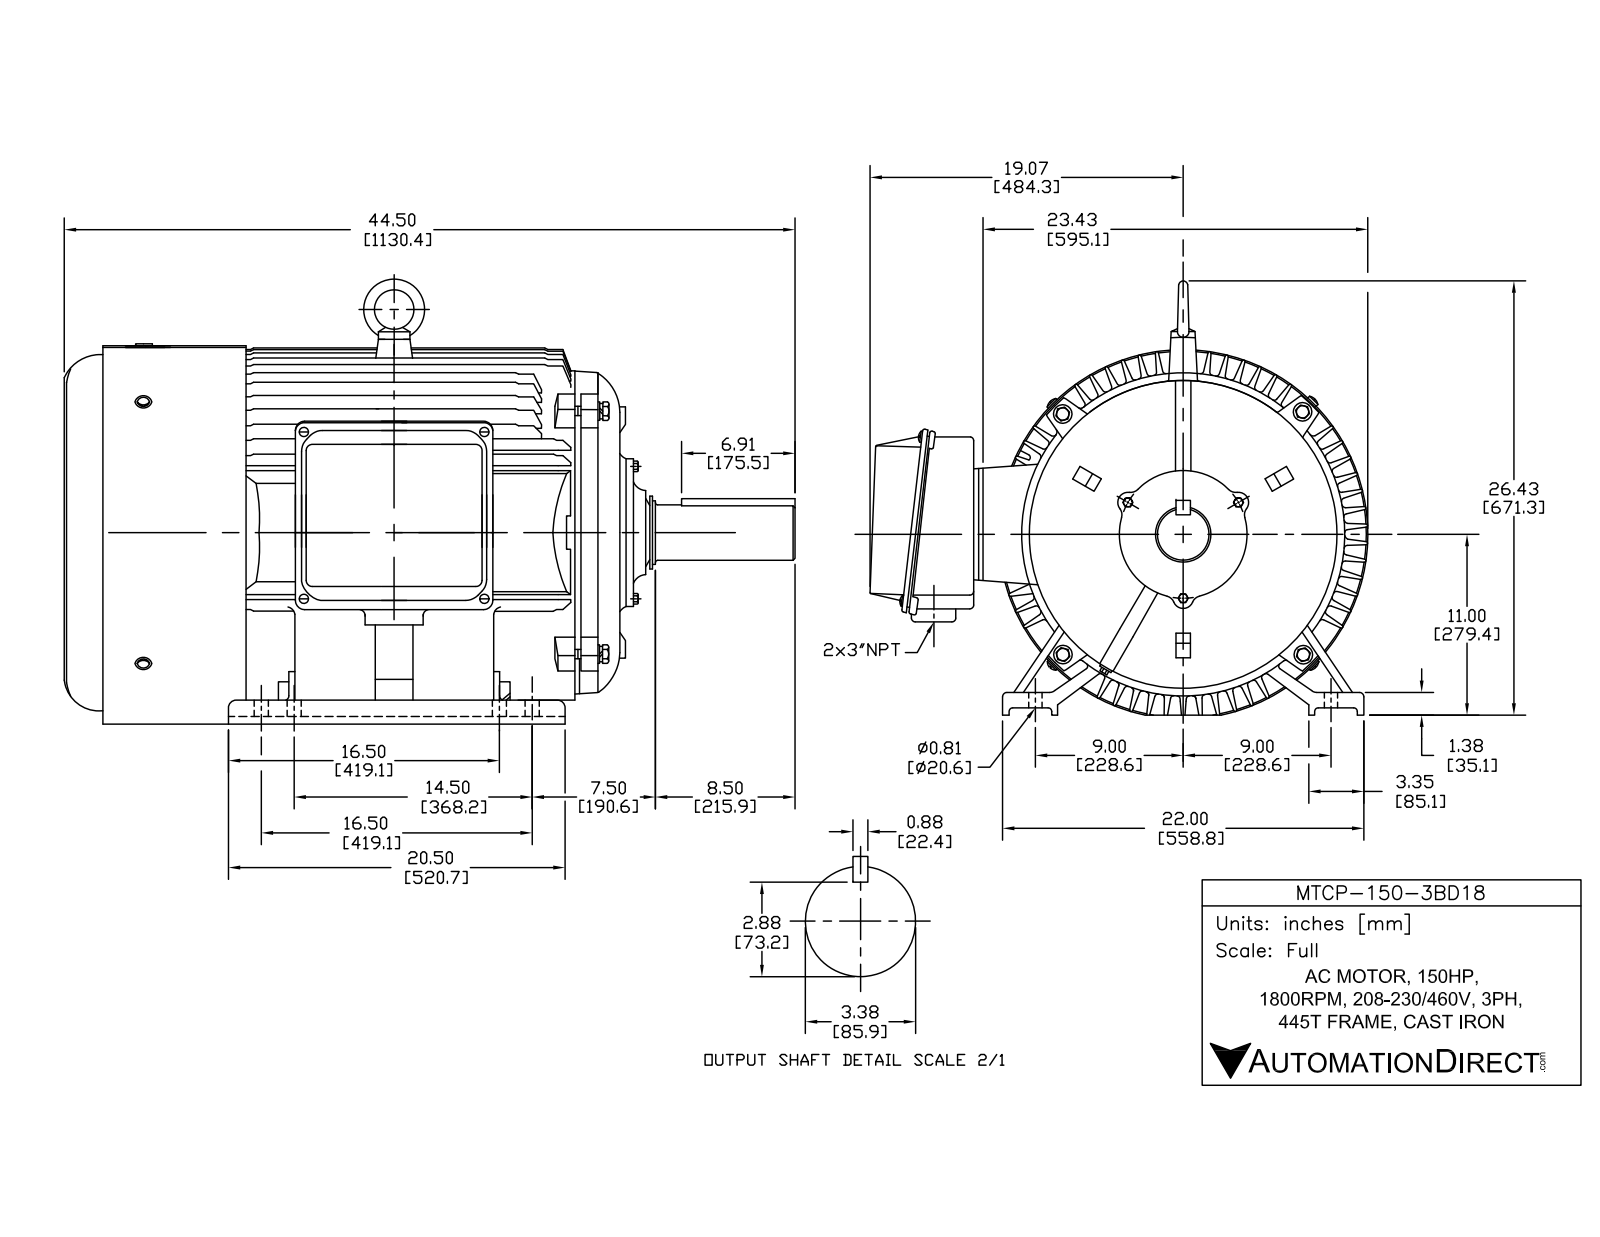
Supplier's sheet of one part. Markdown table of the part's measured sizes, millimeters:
| quantity | value |
| --- | --- |
| part name | plain washers-chamfered--normal series-a gb_GB_FASTENER_WASHER_SWCA 12; BT449橡皮塞; hexagon head bolts-full thread gb_GB_FASTENER_BOLT_STBAB A M10X20-N; hex head bolts-full thread grade c gb_GB_FASTENER_BOLT_HHBFTC M12X65-N (+8 more) |
| STEP written by | SolidWorks 2017 (AUTOMOTIVE_DESIGN) |
| units | millimeters |
| bodies | 68 solids, 4355 faces (1210 planar, 1667 cylindrical, 1478 other) |
| overall size | 1123.4 × 781.17 × 686.1 |
| volume | 38 730 000 mm³ |
| surface area | 7 503 000 mm² |
| round holes (diameter × count) | 12 × 20, 6.8 × 8, 8.5 × 8, 21 × 8, 2.05 × 4, 6 × 4, 8.4 × 4, 8.68 × 4, 9 × 4, 10 × 4, 10.2 × 4, 12.9 × 4 |
| round bosses / shafts (diameter × count) | 10 × 16, 24 × 4, 19.1 × 4, 16 × 4, 12.88 × 4, 12 × 4, 8 × 4, 584 × 1 |
| partial cylindrical surfaces (radius × count) | 1 × 254, 3 × 163, 5 × 93, 2 × 42, 9 × 36, 6 × 33, 10 × 25, 0.75 × 24 |
| main face-to-face distances | 6, 2, 9, 14.7, 37.3, 859.9, 857.9, 40, 868.9, 866.9 |
| hole center spacings | 130, 87.5, 107.5, 99.03, 268, 20, 50.8, 118.56 |
